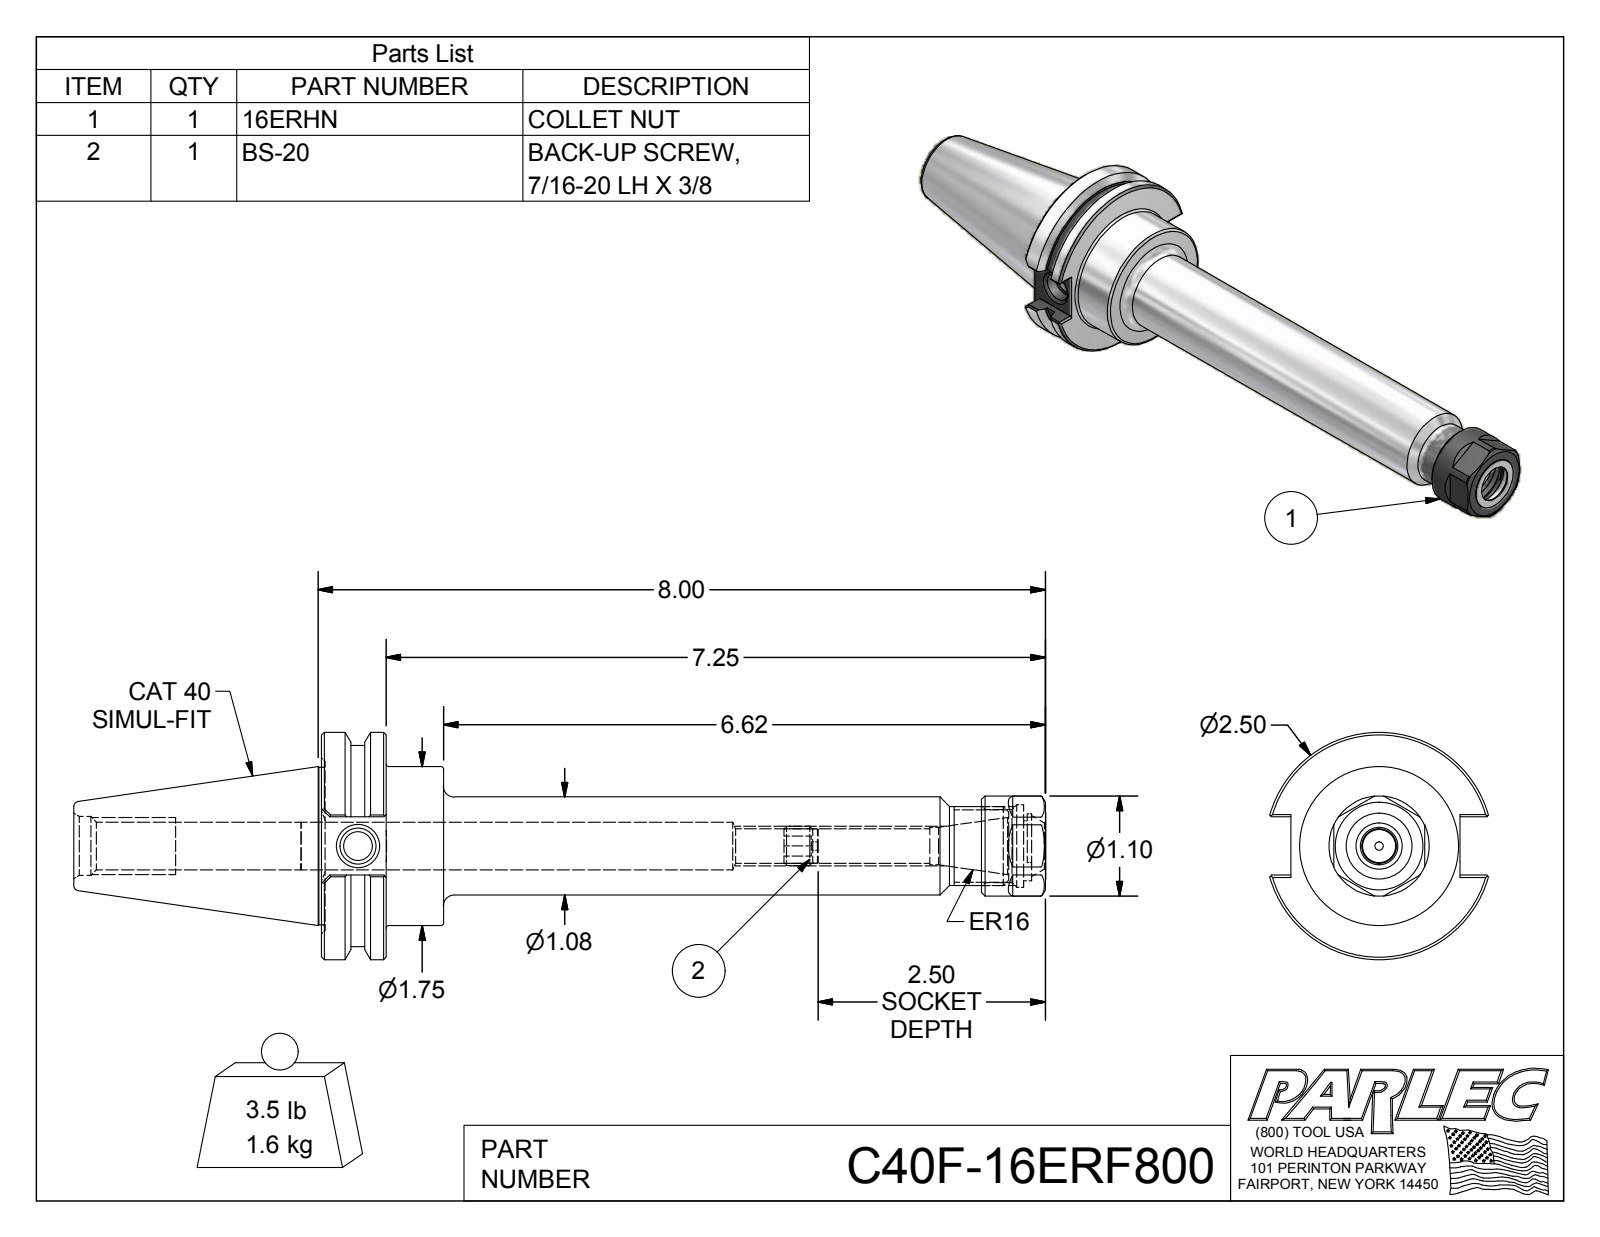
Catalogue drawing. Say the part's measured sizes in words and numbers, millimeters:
The part is named "C40F-16ER8-1; 16ERHN; BS-20; C40F-16ERF800". Its 3-D file was written by "Autodesk Inventor 2016 (AUTOMOTIVE_DESIGN)". It is 3 solids with 129 faces: 59 planar, 26 cylindrical and 44 other. Overall it measures 271.46 by 63.5 by 61.11 millimeters. Its volume is 202 363 cubic millimeters and its surface area 46 442 square millimeters. Round holes: 1 of diameter 2.29, 1 of diameter 8, 1 of diameter 9.73, 1 of diameter 10.13, 1 of diameter 11.18, 1 of diameter 12.4, 1 of diameter 13.38, 1 of diameter 13.39, 1 of diameter 16.46, 1 of diameter 17.02, 1 of diameter 20.5, 1 of diameter 23. Round bosses or shafts: 1 of diameter 63.5, 1 of diameter 56.26, 1 of diameter 44.45, 1 of diameter 28, 1 of diameter 27.43, 1 of diameter 22, 1 of diameter 10.97, 1 of diameter 9.46. Partial cylindrical surfaces (rounded edges, fillets, slot ends): 1 of radius 7.24, 1 of radius 9. The main face-to-face distances are 18.04, 34.04, 16, 202.19, 184.15, 168.15, 25.14, 196.49, 178.45, 162.45. The hole center spacings are 1.52.
